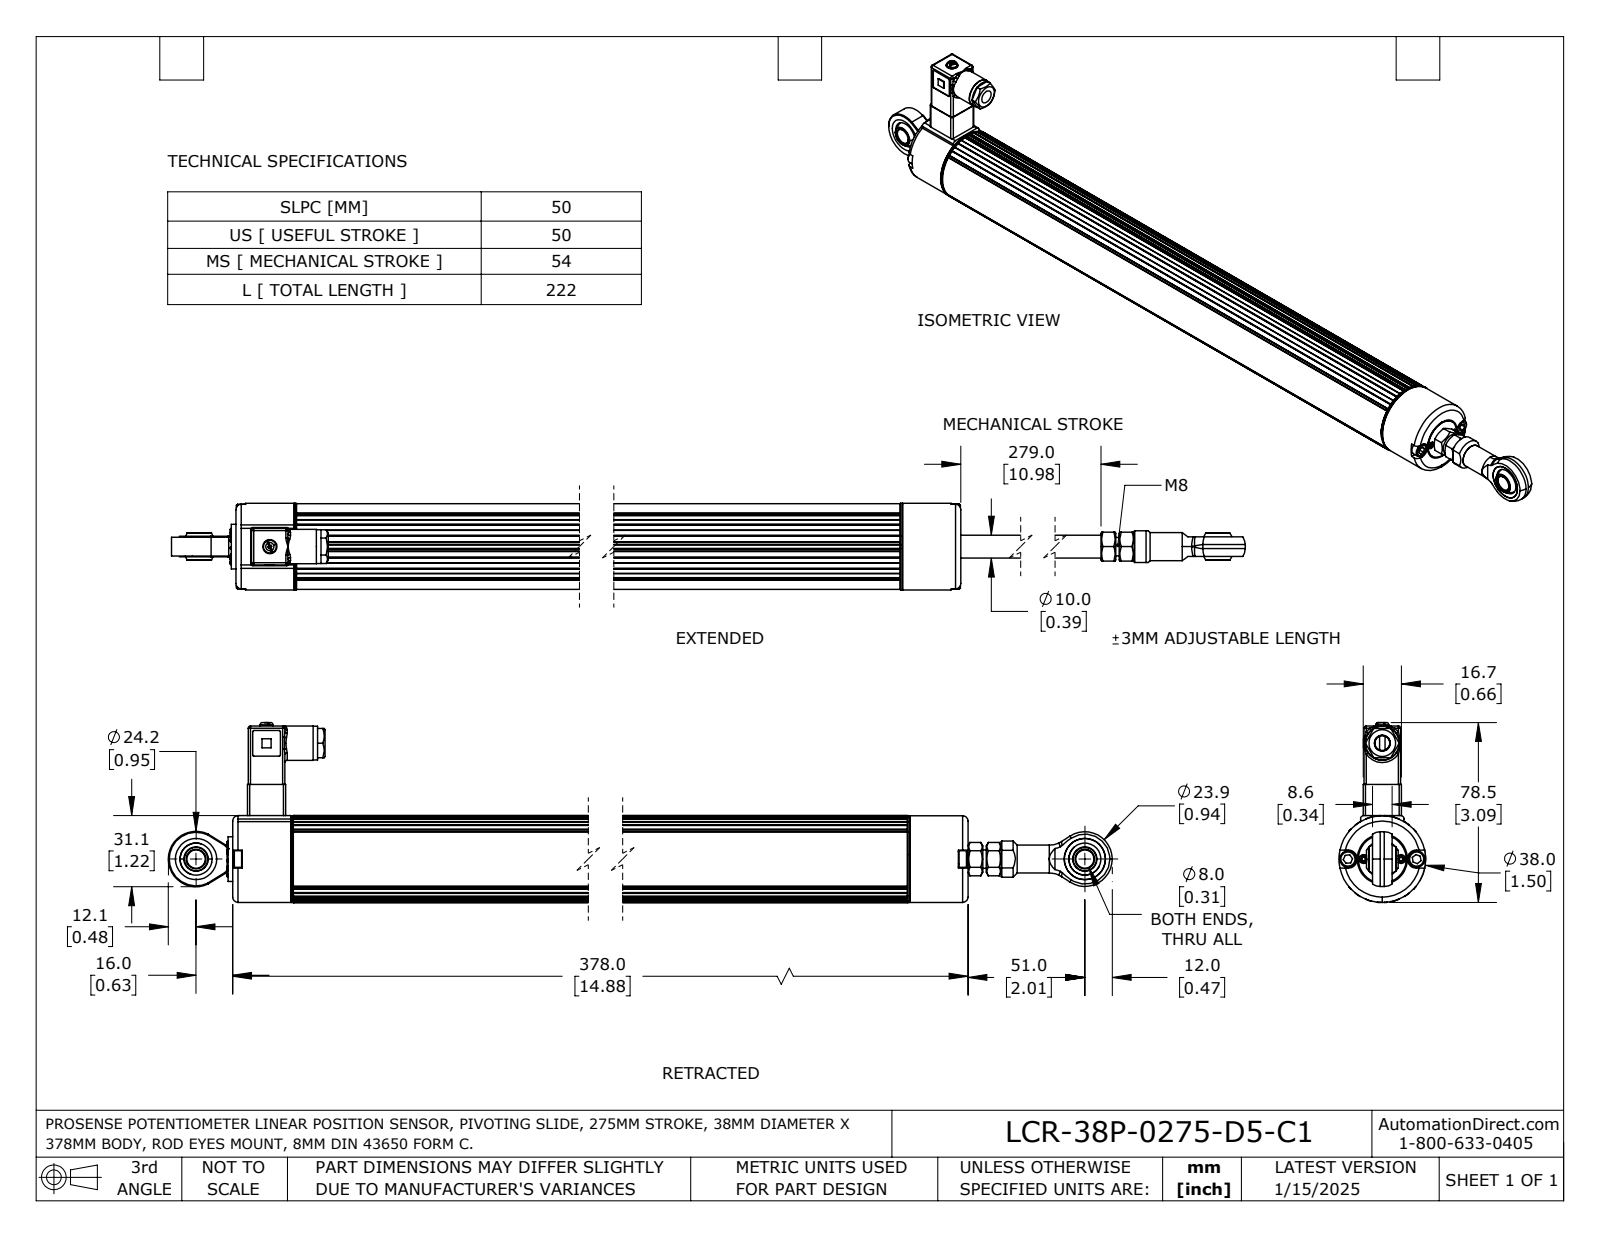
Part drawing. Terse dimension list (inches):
name: LCR-38P-0275-D5-C1
written by: SolidWorks 2023 (AUTOMOTIVE_DESIGN)
unit: in
bodies: 11 solids, 657 faces (295 planar, 210 cylindrical, 152 other)
size: 18.467 × 3.093 × 1.488
volume: 26.63 in³; area: 125.5 in²
holes: 6× ⌀0.102, 4× ⌀0.091, 3× ⌀0.315, 3× ⌀0.551, 2× ⌀0.094, 2× ⌀0.1, 2× ⌀0.111, 2× ⌀0.134, 2× ⌀0.152, 2× ⌀0.165, 1× ⌀0.079, 1× ⌀0.118
bosses: 6× ⌀0.063, 4× ⌀0.283, 4× ⌀0.15, 2× ⌀0.48, 2× ⌀0.079, 1× ⌀1.488, 1× ⌀0.823, 1× ⌀0.768
rounds: 32× R0.008, 20× R0.039, 12× R0.02, 6× R0.016, 2× R0.012, 2× R0.059, 2× R0.083, 2× R0.098
face distances: 12.795, 1.043, 13.839, 0.031, 0.045, 0.612, 0.598, 0.014, 0.644, 0.138
hole spacings: 0.632, 0.075, 0.634, 0.264, 0.268, 0.285, 0.323, 0.394
